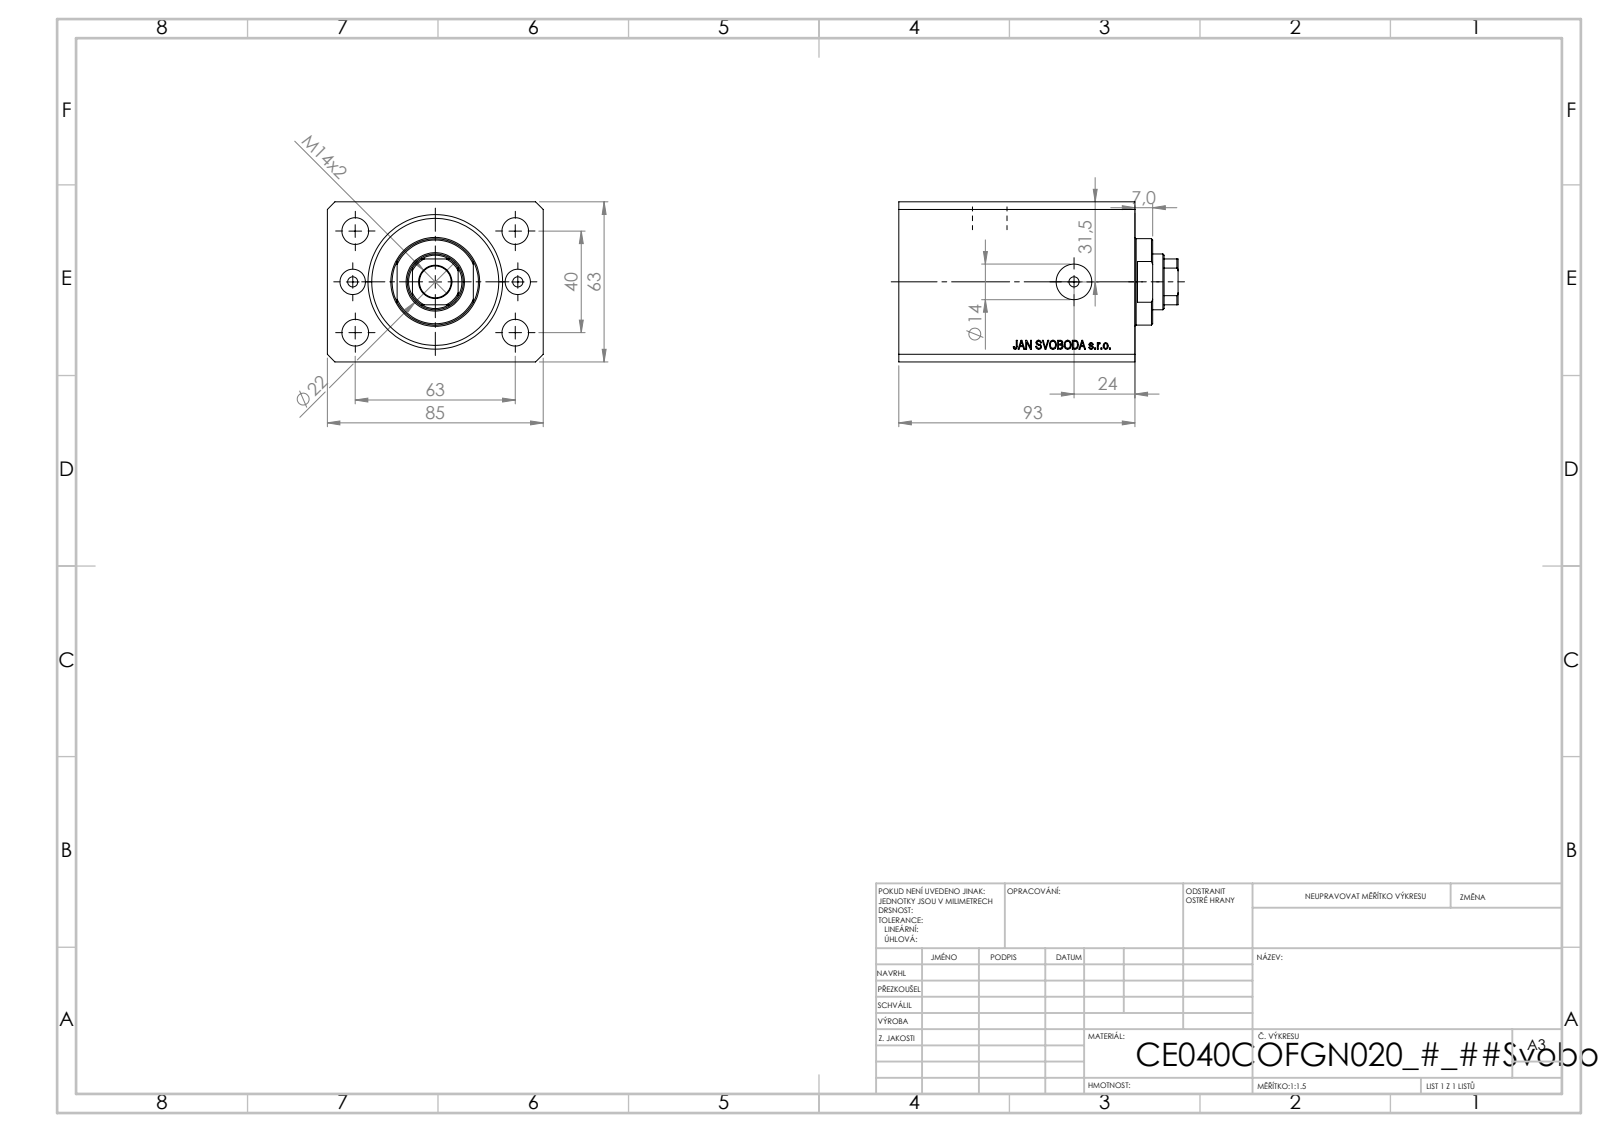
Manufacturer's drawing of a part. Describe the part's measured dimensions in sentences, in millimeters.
The part is named "V250CE_C_Body; V250CE_C_VCP; V250CE_VC_C". Its 3-D file was written by "SolidWorks 2019 (CONFIG_CONTROL_DESIGN)". It is 3 solids with 864 faces: 428 planar, 44 cylindrical and 392 other. Overall it measures 110 by 85 by 63 millimeters. Its volume is 450 054 cubic millimeters and its surface area 83 653 square millimeters. Round holes: 4 of diameter 4, 4 of diameter 10.5, 2 of diameter 10, 2 of diameter 14, 1 of diameter 12.5, 1 of diameter 22, 1 of diameter 40, 1 of diameter 53. Round bosses or shafts: 1 of diameter 34. Partial cylindrical surfaces (rounded edges, fillets, slot ends): 1 of radius 10.5. The main face-to-face distances are 63, 85, 93, 17, 76, 11.4, 64.6, 81.6, 56, 44.6. The hole center spacings are 20.02, 37.31, 67.05, 32.5, 40, 63, 74.63, 45.
